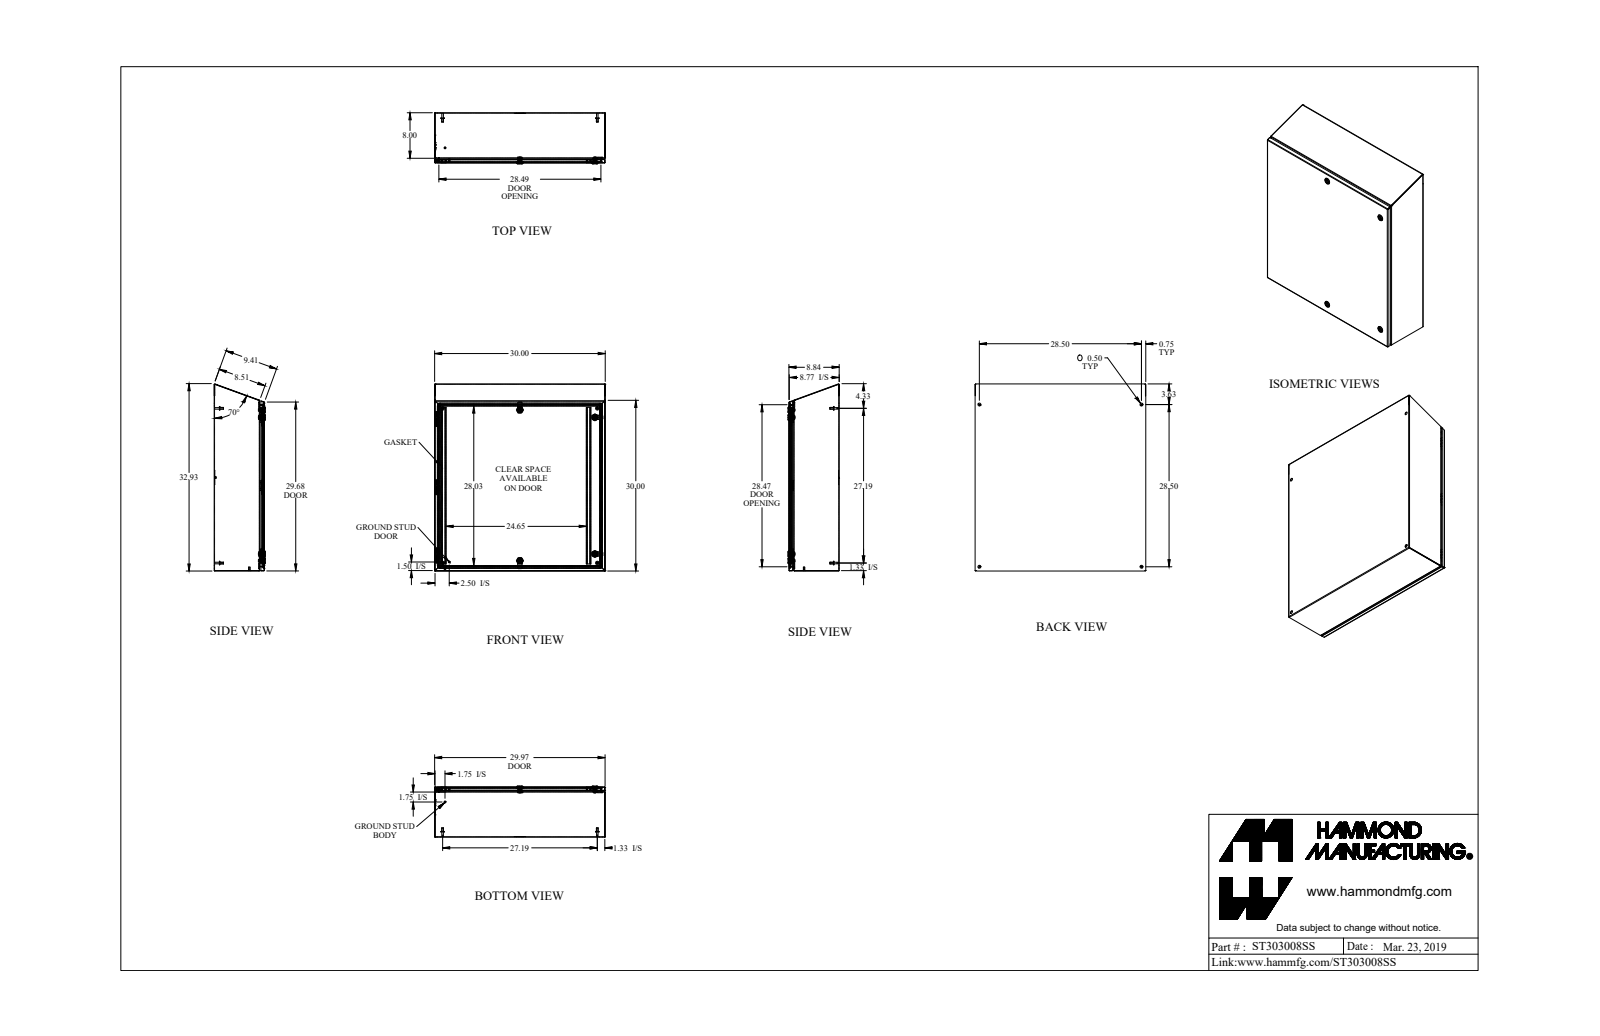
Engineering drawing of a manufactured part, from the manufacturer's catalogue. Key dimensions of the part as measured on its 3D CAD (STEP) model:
Part name (STEP PRODUCT): ST303008SS
STEP written by: SolidWorks 2018 (AUTOMOTIVE_DESIGN)
Units: inches
Bodies: 45 solids, 1421 faces (753 planar, 355 cylindrical, 313 other)
Overall size (bounding box): 32.883 × 30 × 8.997
Volume: 241.5 in³ · Surface area: 6 770 in²
Round holes (diameter × count): ⌀0.5 ×8, ⌀0.197 ×4, ⌀0.387 ×4, ⌀0.63 ×4, ⌀0.768 ×4, ⌀0.172 ×1, ⌀0.24 ×1, ⌀0.242 ×1
Round bosses / shafts (diameter × count): ⌀0.625 ×8, ⌀0.313 ×6, ⌀1.1 ×4, ⌀0.785 ×4, ⌀0.525 ×4, ⌀0.275 ×4, ⌀0.236 ×4, ⌀0.25 ×2
Partial cylindrical surfaces — rounded edges, fillets, slot ends (radius × count): R0.036 ×20, R0.108 ×20, R0.01 ×12, R0.048 ×12, R0.25 ×11, R0.125 ×8, R0.375 ×8, R0.006 ×6
Main face-to-face distances: 0.072, 8.765, 8.693, 8.837, 29.928, 29.856, 30, 7.928, 0.837, 8
Hole centre spacings: 28.5, 2.493, 26.272, 27.518, 37.964, 40.305, 13.242, 13.253
